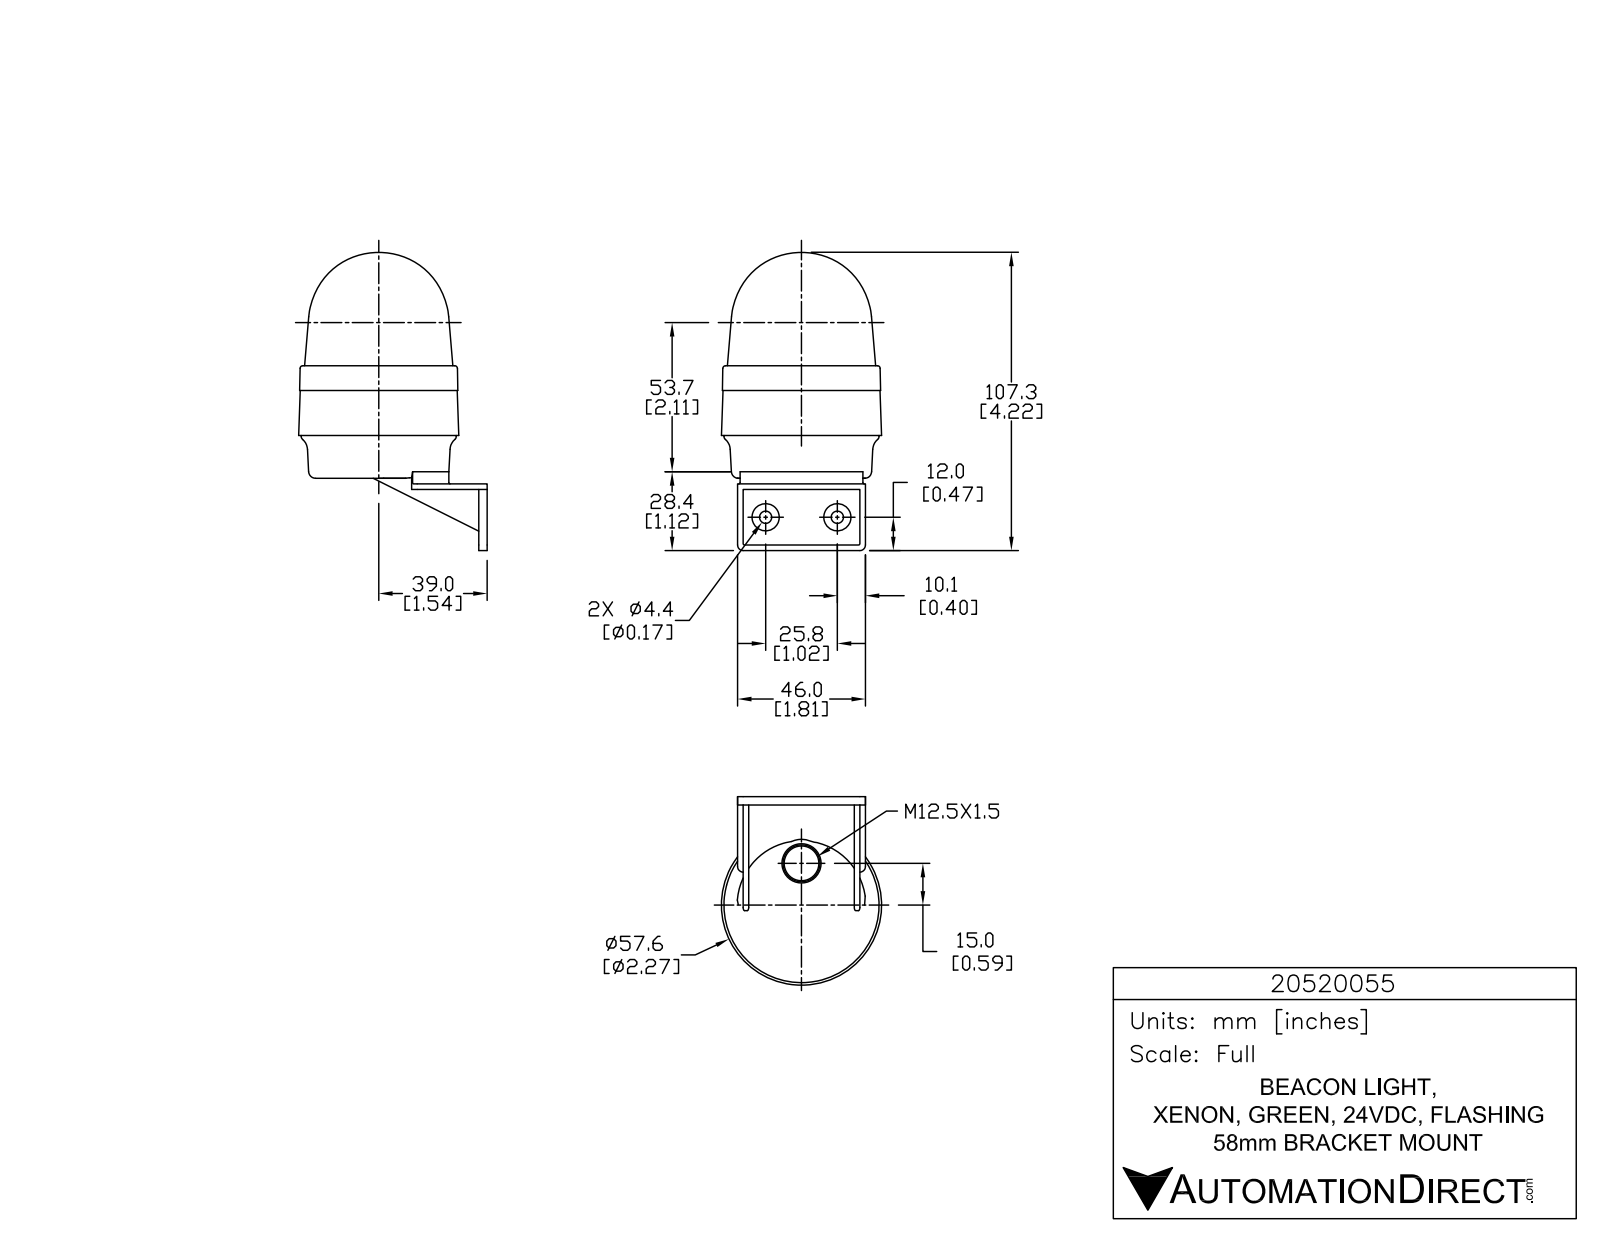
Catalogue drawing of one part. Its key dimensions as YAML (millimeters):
part_name: "20520055"
step_written_by: "SolidWorks 2015 (AUTOMOTIVE_DESIGN)"
units: millimeters
bodies: {solids: 1, faces: 828, planar: 551, cylindrical: 179, other: 98}
overall_size: [107.3, 72.4, 61.1]
volume: 168300
surface_area: 21540
round_holes:
  - {diameter: 1, count: 3}
  - {diameter: 4.4, count: 2}
round_bosses_or_shafts:
  - {diameter: 5.7, count: 3}
  - {diameter: 1.4, count: 3}
  - {diameter: 9.8, count: 2}
  - {diameter: 55.8, count: 1}
partial_cylinders:
  - {radius: 0.2, count: 6}
  - {radius: 0.2, count: 6}
  - {radius: 0.2, count: 6}
  - {radius: 0.5, count: 6}
  - {radius: 3.3, count: 6}
  - {radius: 2, count: 4}
  - {radius: 0.1, count: 3}
  - {radius: 0.1, count: 3}
face_to_face_distances: [2, 4, 40, 42, 1, 3, 38, 22, 24, 19.4]
hole_center_spacings: [25.8]
